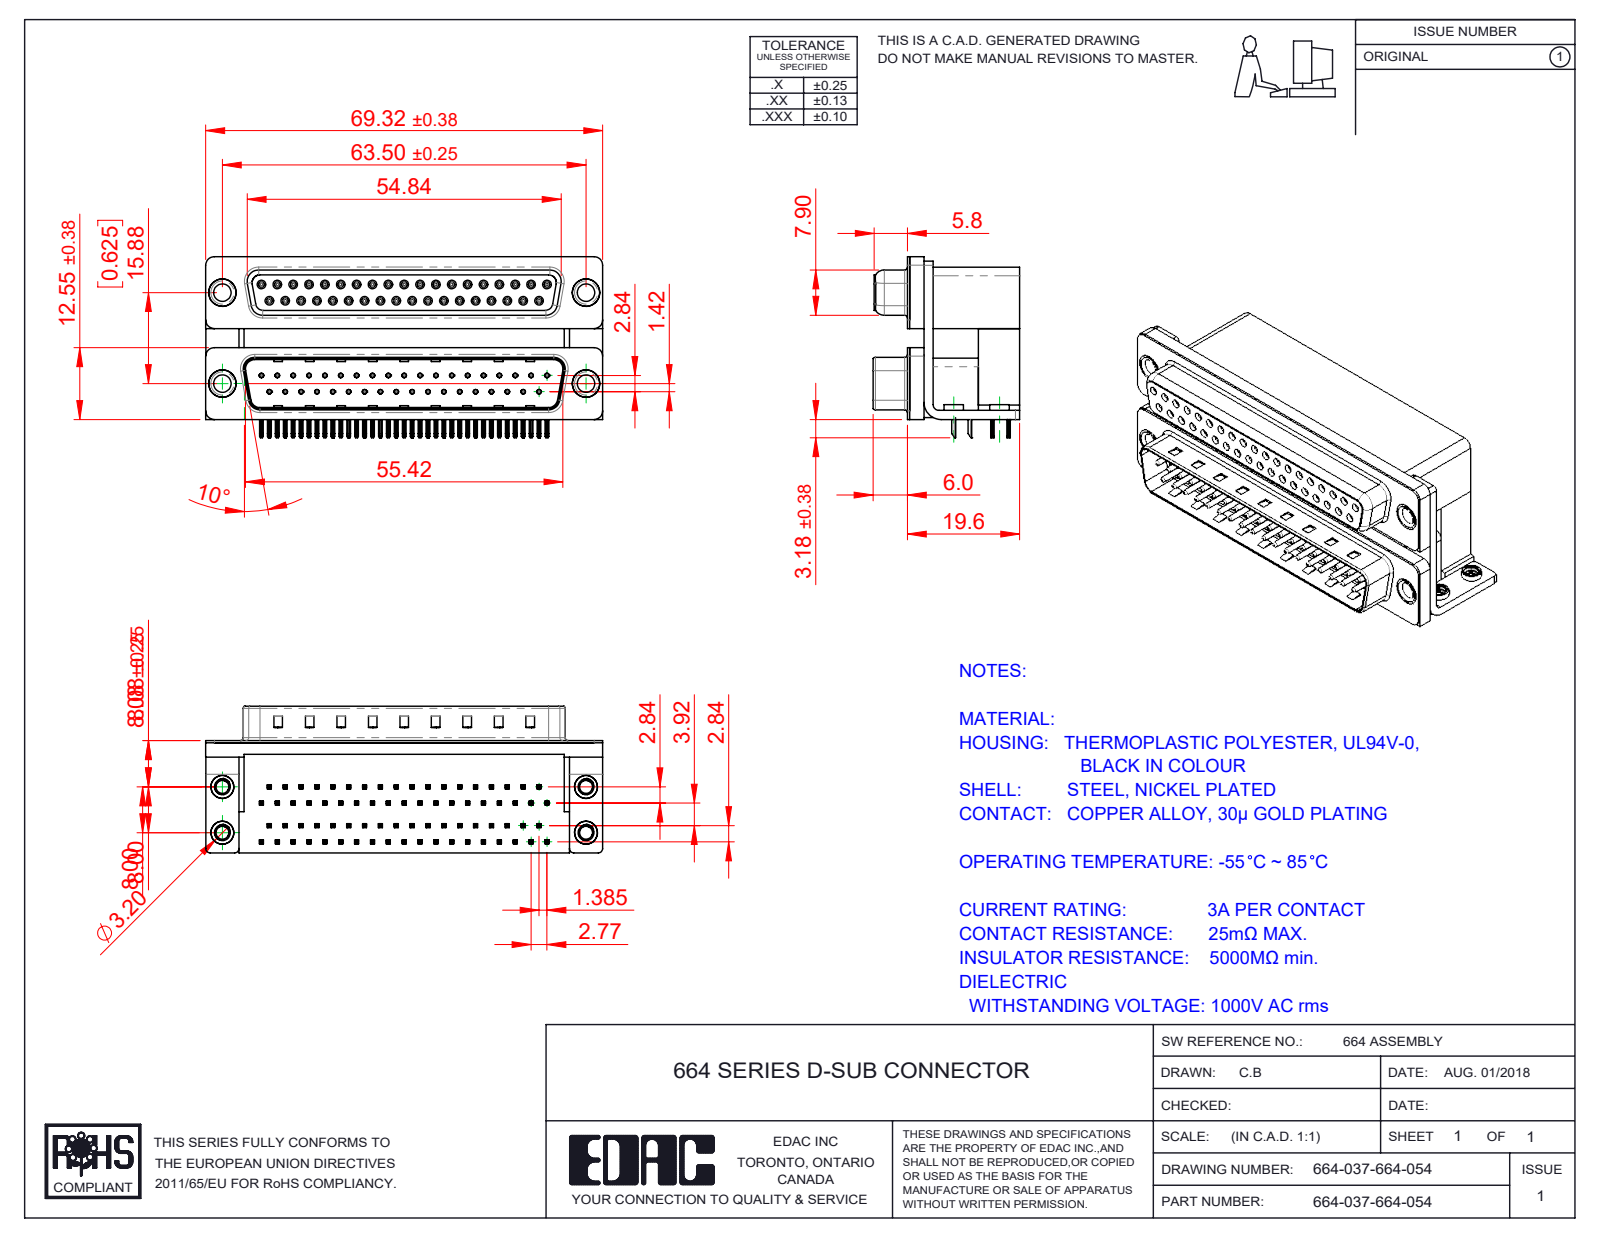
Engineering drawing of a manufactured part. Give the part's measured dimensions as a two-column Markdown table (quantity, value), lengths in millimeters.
| quantity | value |
| --- | --- |
| part name | 664-037-664-054; 664 Contact Bottom Upper_L; 664 Contact Top Upper_L; 664 Housing Upper_37 Contacts L (+8 more) |
| STEP written by | SolidWorks 2020 (CONFIG_CONTROL_DESIGN) |
| units | millimeters |
| bodies | 89 solids, 9001 faces (4753 planar, 2217 cylindrical, 2031 other) |
| overall size | 69.32 × 31.61 × 25.6 |
| volume | 29 802 mm³ |
| surface area | 31 653 mm² |
| round holes (diameter × count) | 0.8 × 74, 0.35 × 37, 0.9 × 37, 2.26 × 4, 2.75 × 4, 3.05 × 4, 3.2 × 4, 3.5 × 4, 4 × 4, 4.8 × 4, 5 × 4 |
| round bosses / shafts (diameter × count) | 1.2 × 37, 0.75 × 37, 4.9 × 4, 4.75 × 4, 4 × 4, 3.85 × 4, 3.4 × 4 |
| partial cylindrical surfaces (radius × count) | 0.1 × 296, 0.15 × 148, 0.25 × 148, 0.12 × 74, 0.35 × 74, 0.34 × 37, 0.28 × 18, 1.5 × 13 |
| main face-to-face distances | 0.4, 19.2, 7.2, 12, 2.19, 15.52, 2.84, 26.22, 10.7, 13.33 |
| hole center spacings | 2.77, 5.54, 3.16, 8.31, 11.08, 13.85, 16.62, 19.39 |
